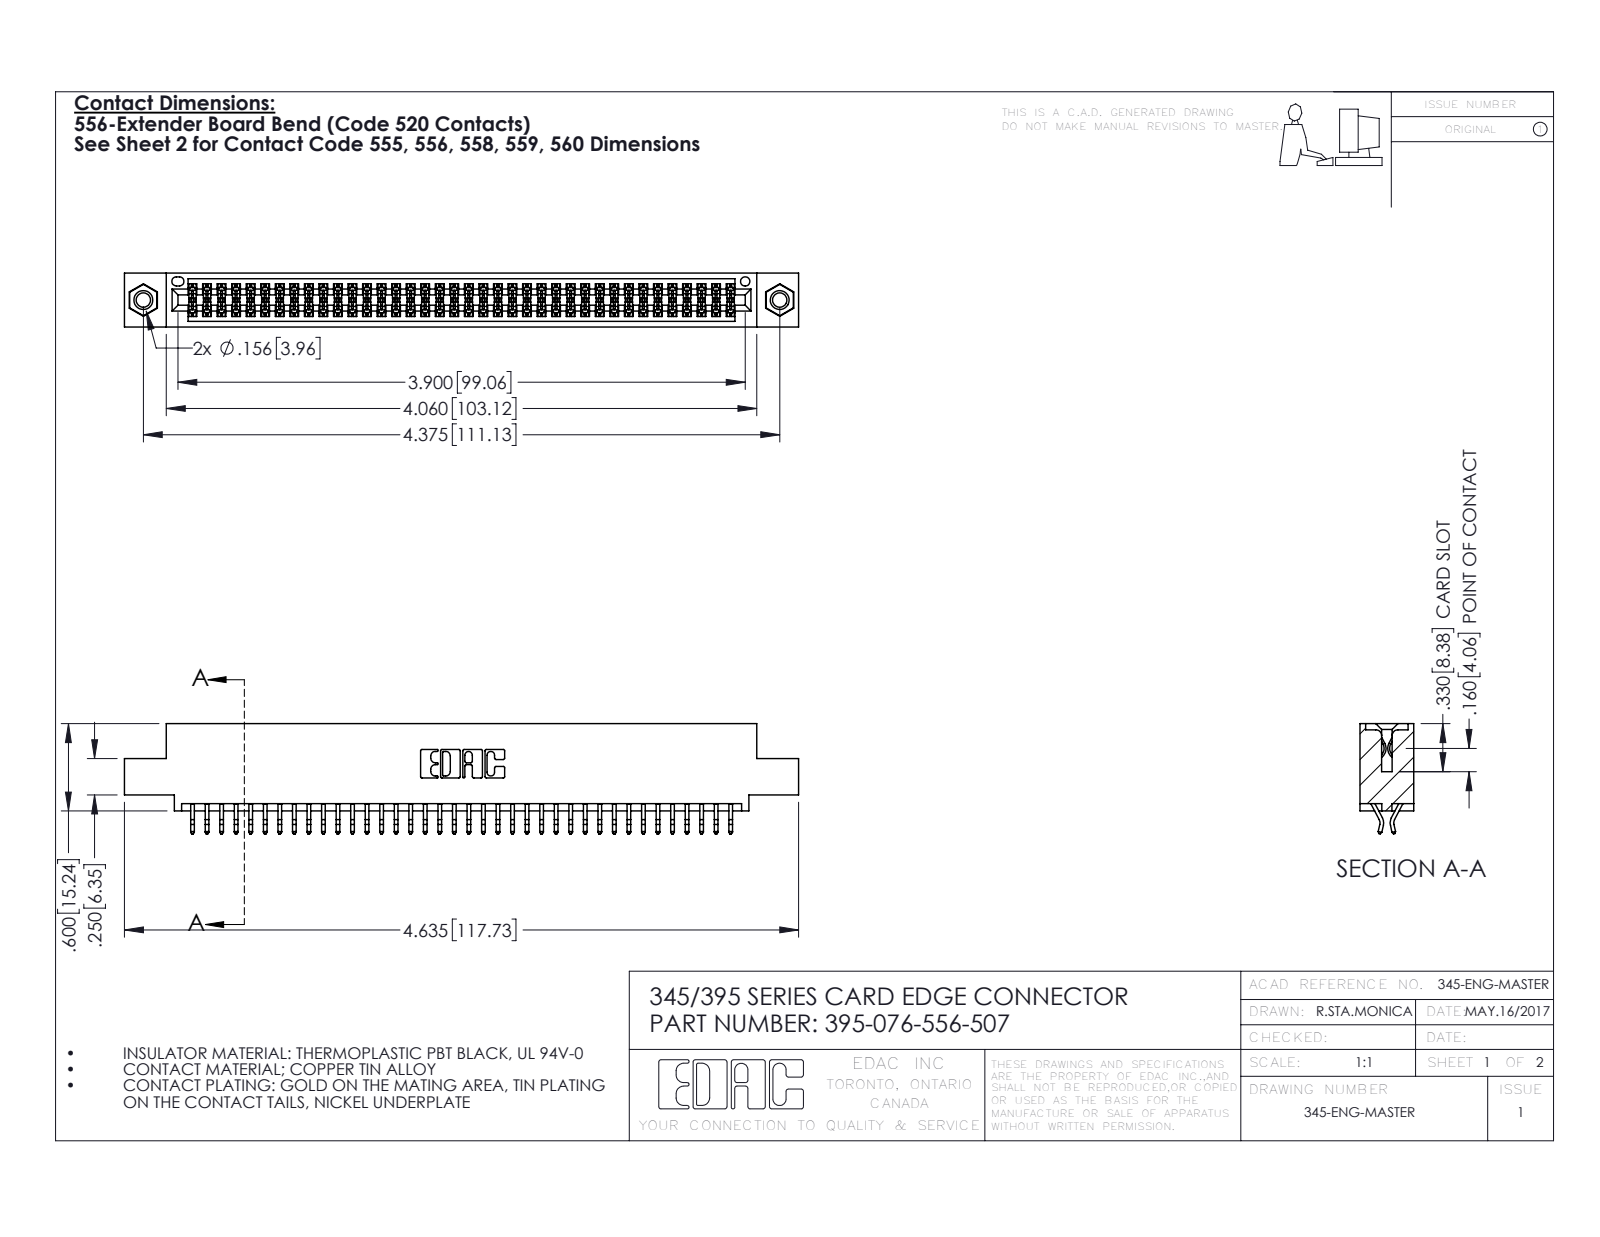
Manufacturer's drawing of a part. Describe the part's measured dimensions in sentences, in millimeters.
The part is named "345-250-001_345-250-005-103; 345 Part_0.110 Offset - 0.156 Dia-TI; 345-292-001_556 Tail; 395-076-556-507". Its 3-D file was written by "SolidWorks 2016 (CONFIG_CONTROL_DESIGN)". It is 79 solids with 4446 faces: 2928 planar, 1502 cylindrical and 16 other. Overall it measures 117.7 by 19.2 by 9.4 millimeters. Its volume is 11 300 cubic millimeters and its surface area 16 700 square millimeters. Round holes: 2 of diameter 2.5, 2 of diameter 3.2, 2 of diameter 4, 1 of diameter 1.6. Round bosses or shafts: 2 of diameter 3.9. Partial cylindrical surfaces (rounded edges, fillets, slot ends): 114 of radius 0.2, 22 of radius 0.3, 6 of radius 0.2, 6 of radius 0.8, 3 of radius 0.7, 2 of radius 0.3, 2 of radius 0.4, 2 of radius 0.5. The main face-to-face distances are 1.8, 7.6, 9.4, 5.1, 0.6, 2.5, 6.9, 5.7, 4.4, 3.8. The hole center spacings are 6.9, 105.1, 111.1.
